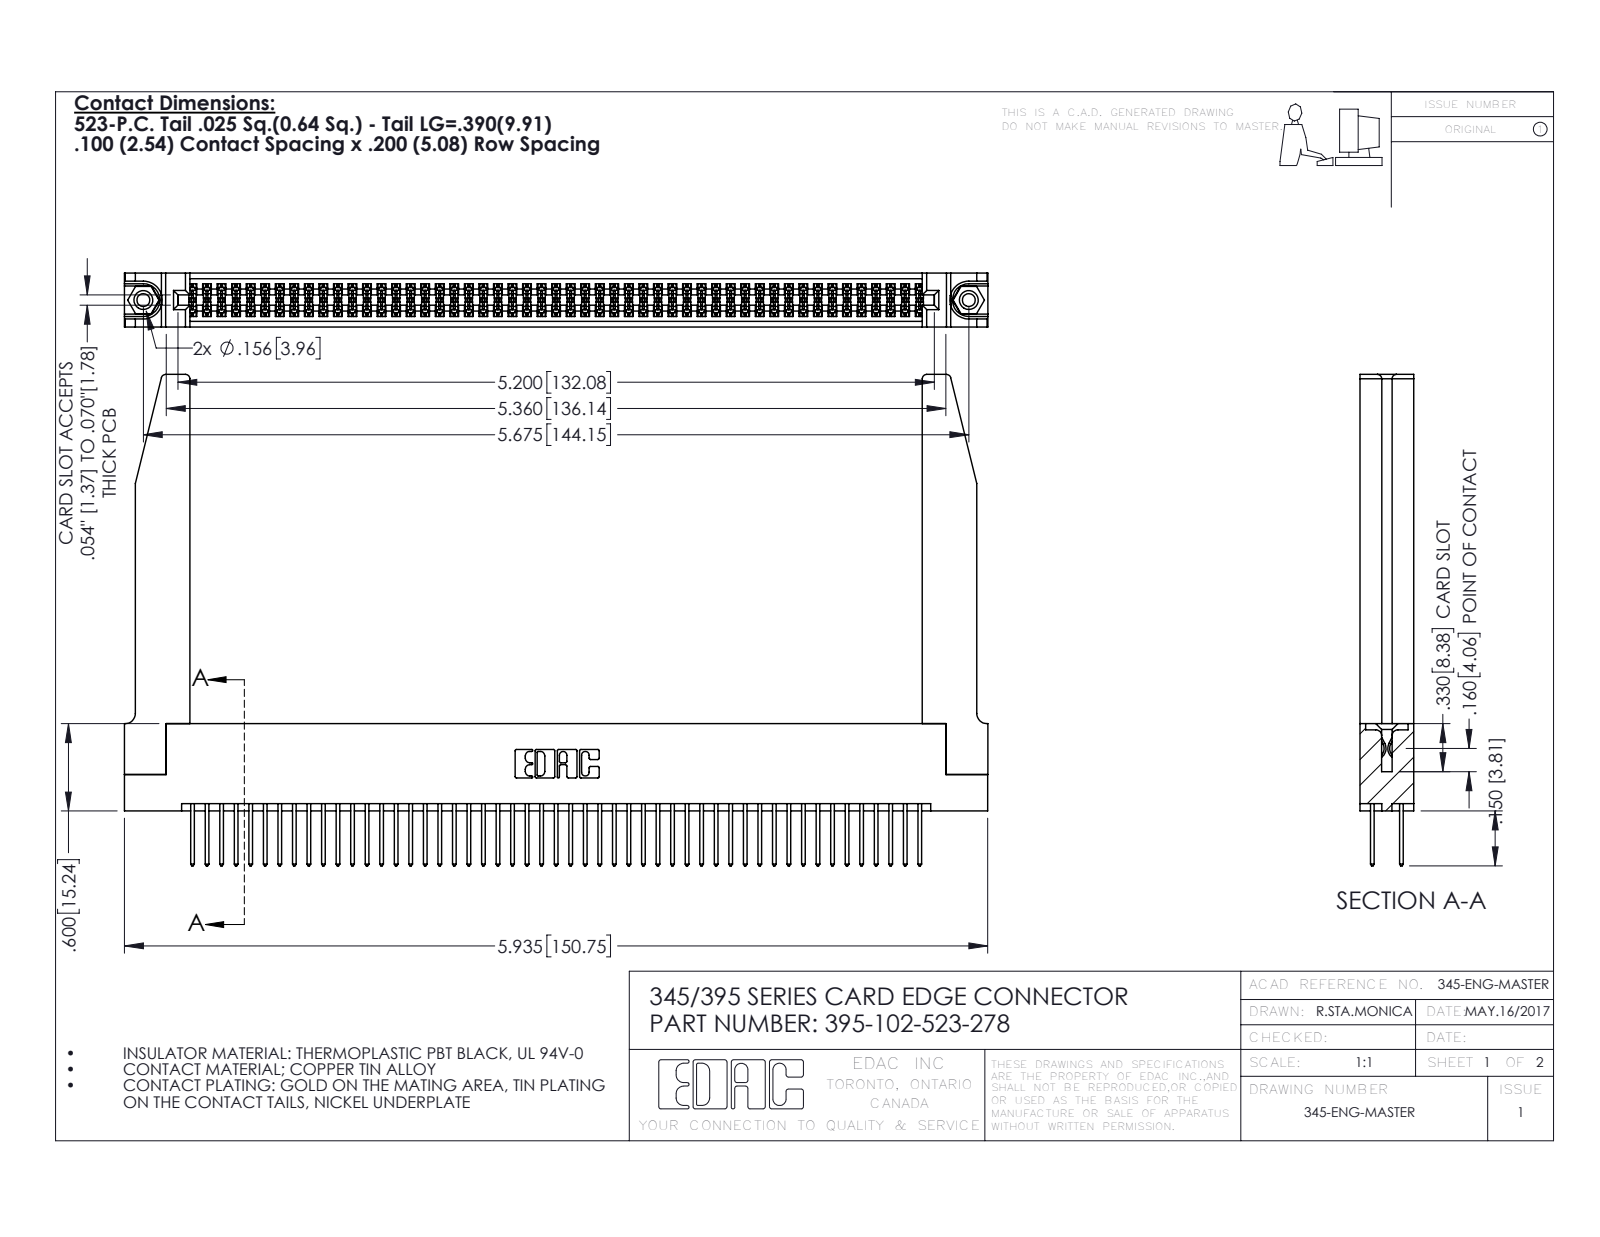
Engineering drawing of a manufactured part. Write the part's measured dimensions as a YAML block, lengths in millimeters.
part_name: "345-220-078_345-220-078; 395-102-523-278; 345 Part_Flush Mounting Lugs - 0.156 Dia-TH; 345-250-001_345-250-001-102 (+1 more)"
step_written_by: "SolidWorks 2016 (CONFIG_CONTROL_DESIGN)"
units: millimeters
bodies: {solids: 107, faces: 5460, planar: 3588, cylindrical: 1820, other: 52}
overall_size: [150.8, 85.8, 9.4]
volume: 22710
surface_area: 30030
round_holes:
  - {diameter: 2.3, count: 2}
  - {diameter: 3.2, count: 2}
  - {diameter: 4, count: 2}
  - {diameter: 1.6, count: 1}
round_bosses_or_shafts:
  - {diameter: 3.9, count: 2}
partial_cylinders:
  - {radius: 0.2, count: 153}
  - {radius: 0.3, count: 102}
  - {radius: 0.3, count: 22}
  - {radius: 0.8, count: 8}
  - {radius: 0.2, count: 6}
  - {radius: 0.8, count: 6}
  - {radius: 0.7, count: 3}
  - {radius: 0.4, count: 2}
face_to_face_distances: [1.8, 7.6, 9.4, 5.1, 2.5, 6.9, 0.6, 5.7, 4.4, 3.8]
hole_center_spacings: [6.9, 138.2, 144.1]
